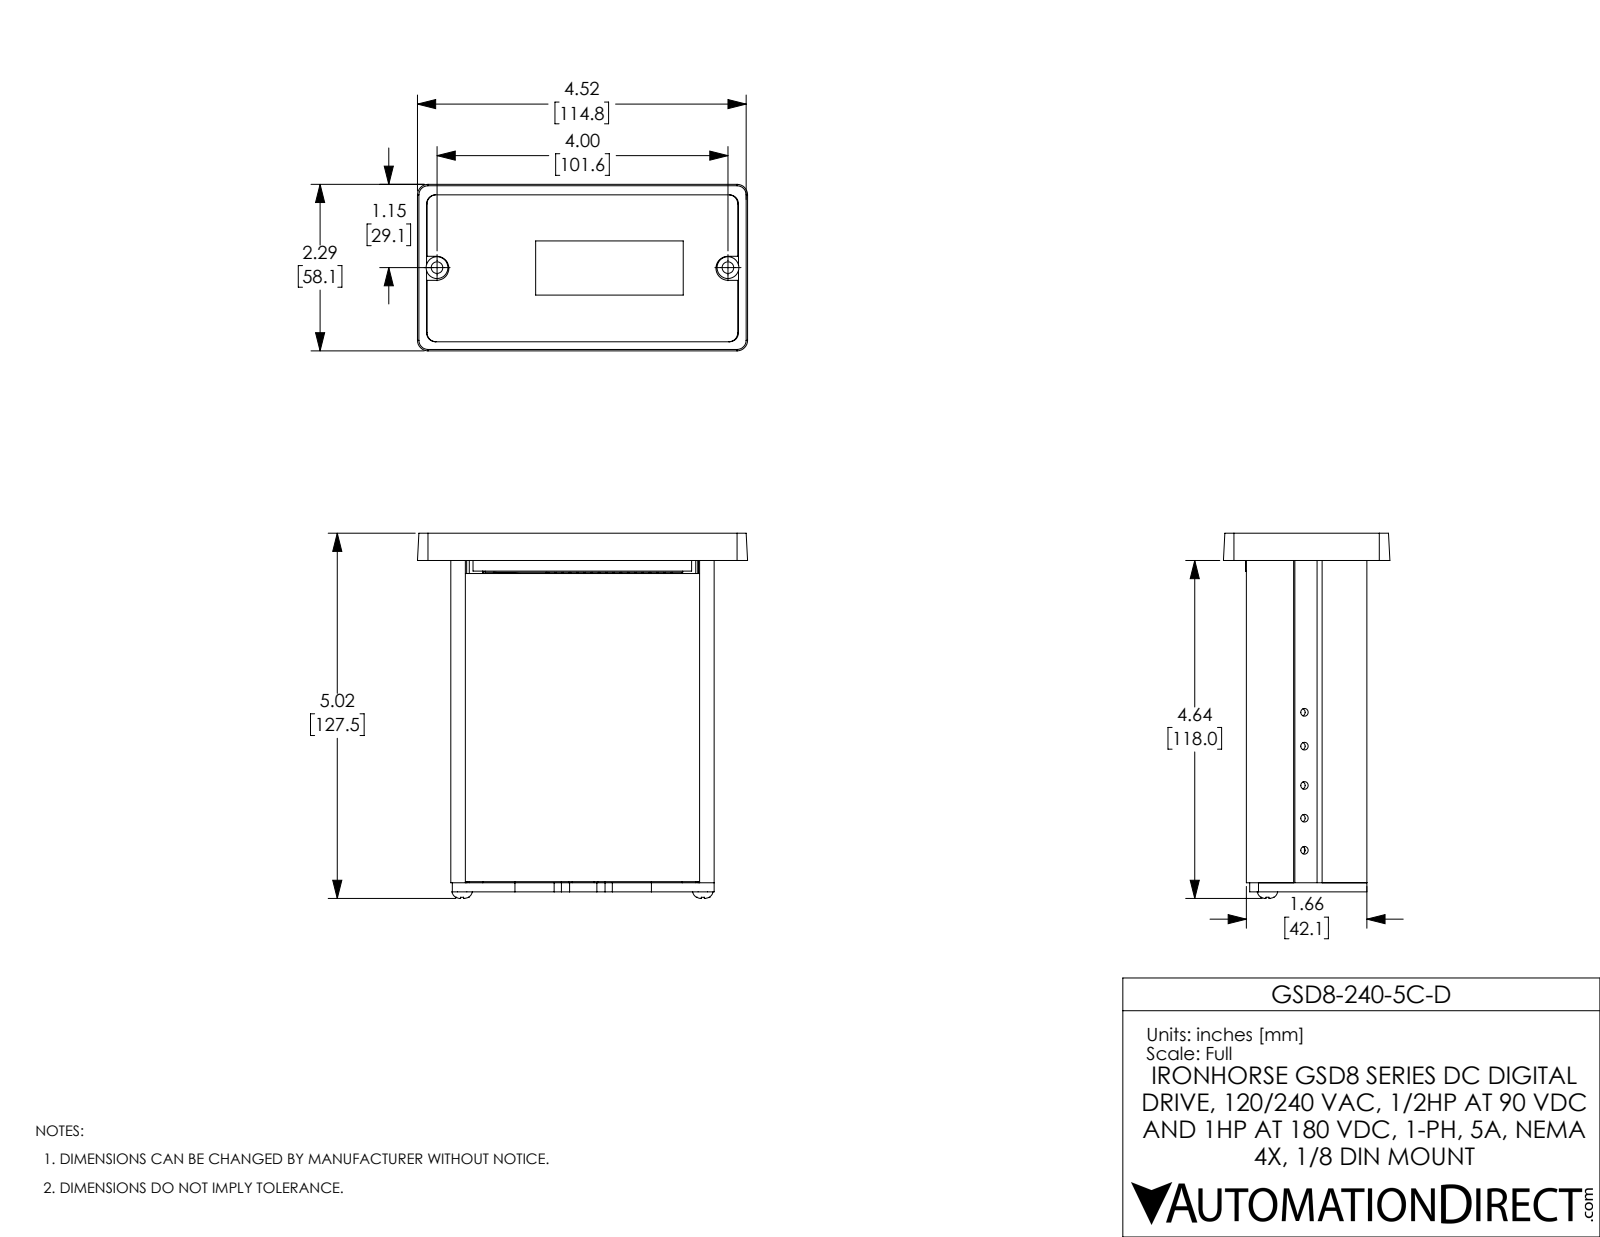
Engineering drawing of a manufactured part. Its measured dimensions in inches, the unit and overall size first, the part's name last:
Units: inches
Overall size (bounding box): 5.019 × 4.539 × 2.289
Round holes (diameter × count): ⌀0.033 ×36, ⌀0.035 ×13, ⌀0.157 ×12, ⌀0.02 ×6, ⌀0.059 ×6, ⌀0.147 ×6, ⌀0.16 ×6, ⌀0.106 ×5, ⌀0.12 ×4, ⌀0.285 ×4, ⌀0.016 ×3, ⌀0.112 ×3
Round bosses / shafts (diameter × count): ⌀0.02 ×36, ⌀0.247 ×3, ⌀0.134 ×2
Partial cylindrical surfaces — rounded edges, fillets, slot ends (radius × count): R0.05 ×18, R0.039 ×16, R0.125 ×12, R0.126 ×10, R0.025 ×7, R0.016 ×4, R0.035 ×4, R0.045 ×4
Main face-to-face distances: 0.1, 1.521, 0.045, 1.566, 1.421, 1.466, 0.031, 1.313, 0.209, 0.178
Hole centre spacings: 0.197, 0.394, 0.591, 0.787, 0.984, 1.181, 0.1, 0.2
Volume: 9.053 in³ · Surface area: 219 in²
Bodies: 15 solids, 1227 faces (759 planar, 447 cylindrical, 21 other)
Part name (STEP PRODUCT): GSD8-240-5C-D
STEP written by: SolidWorks 2017 (AUTOMOTIVE_DESIGN)
